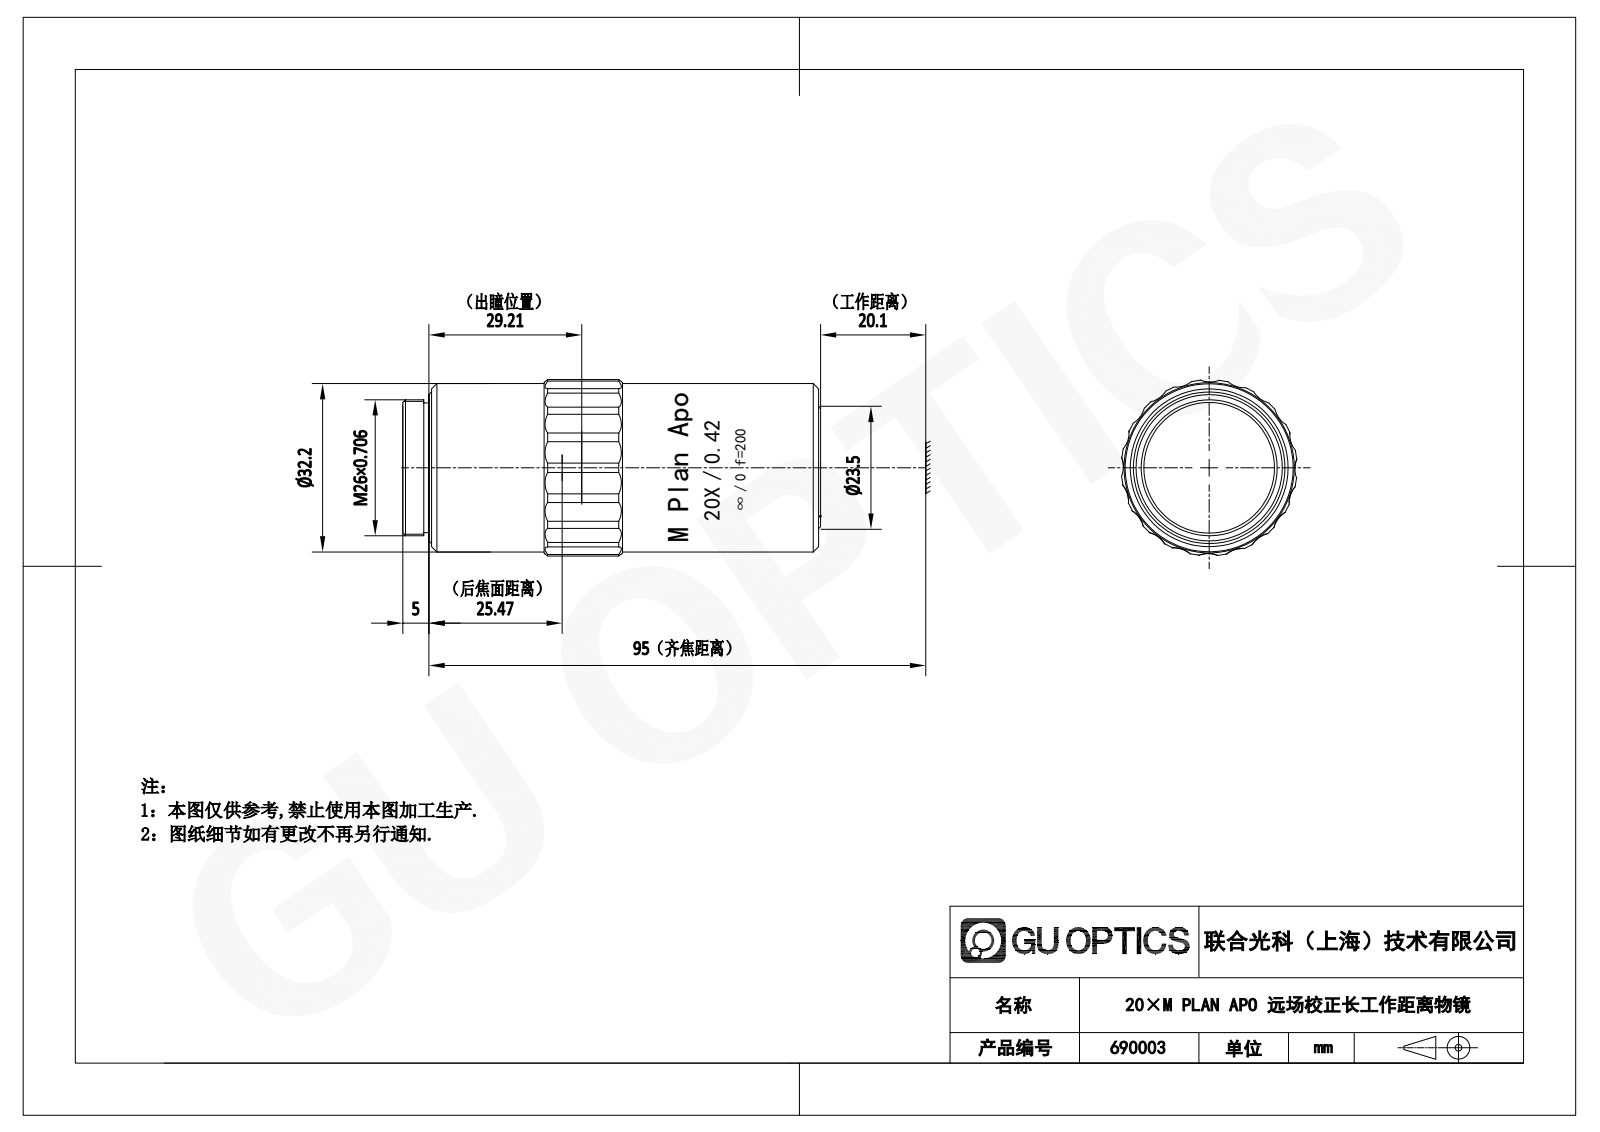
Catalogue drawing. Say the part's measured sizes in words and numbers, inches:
The part is named "690003". Its 3-D file was written by "SolidWorks 2020 (AUTOMOTIVE_DESIGN)". It is 1 solid with 76 faces: 5 planar, 25 cylindrical and 46 other. Overall it measures 3.146 by 1.322 by 1.322 inches. Its volume is 3.91 cubic inches and its surface area 14.98 square inches. Round bosses or shafts: 1 of diameter 0.976. Partial cylindrical surfaces (rounded edges, fillets, slot ends): 20 of radius 0.188. The main face-to-face distances are 0.02, 0.059, 0.039, 0.846, 0.866, 0.906, 0.591, 1.437, 1.457, 1.496.
